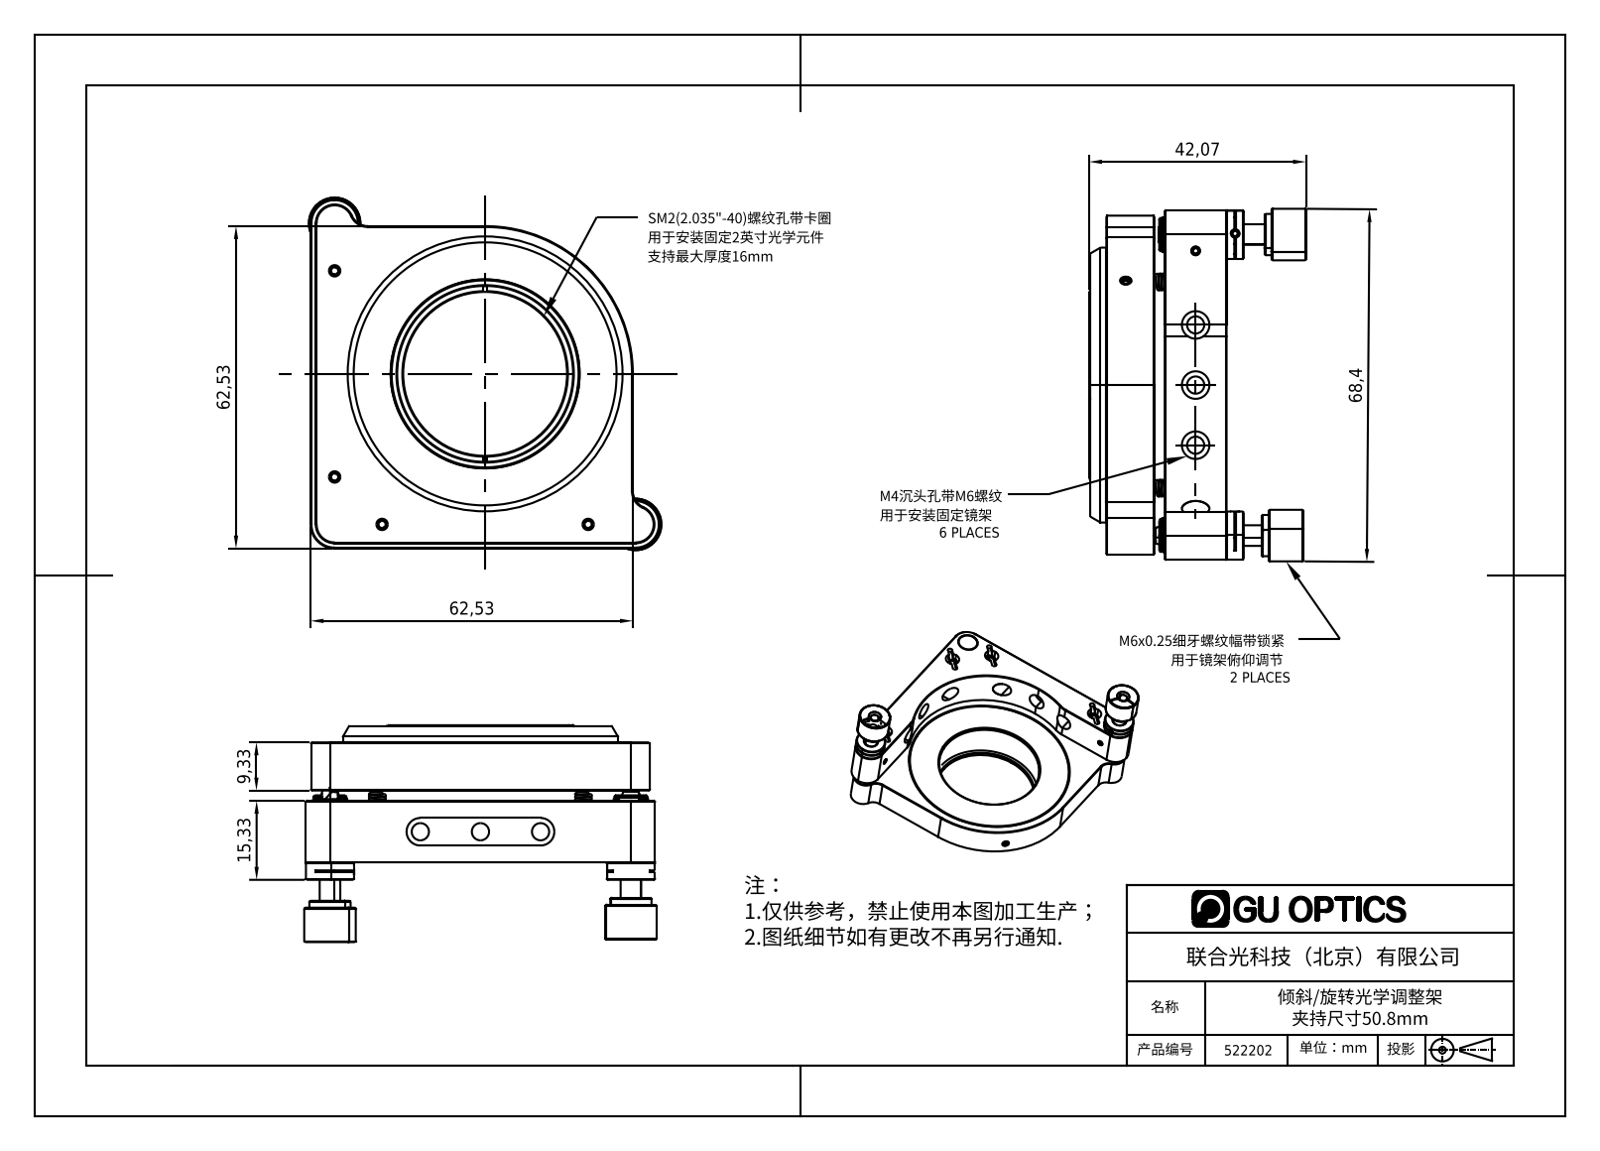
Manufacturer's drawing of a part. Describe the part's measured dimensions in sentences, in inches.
Its 3-D file was written by "SolidWorks 2020 (CONFIG_CONTROL_DESIGN)". It is 1 solid with 474 faces: 169 planar, 0 cylindrical and 305 other. Overall it measures 4.039 by 4.039 by 2.484 inches. The main face-to-face distances are 0.551, 0.709, 0.059, 1.378, 0.827, 0.669, 0.118, 1.563, 0.854, 0.736.
